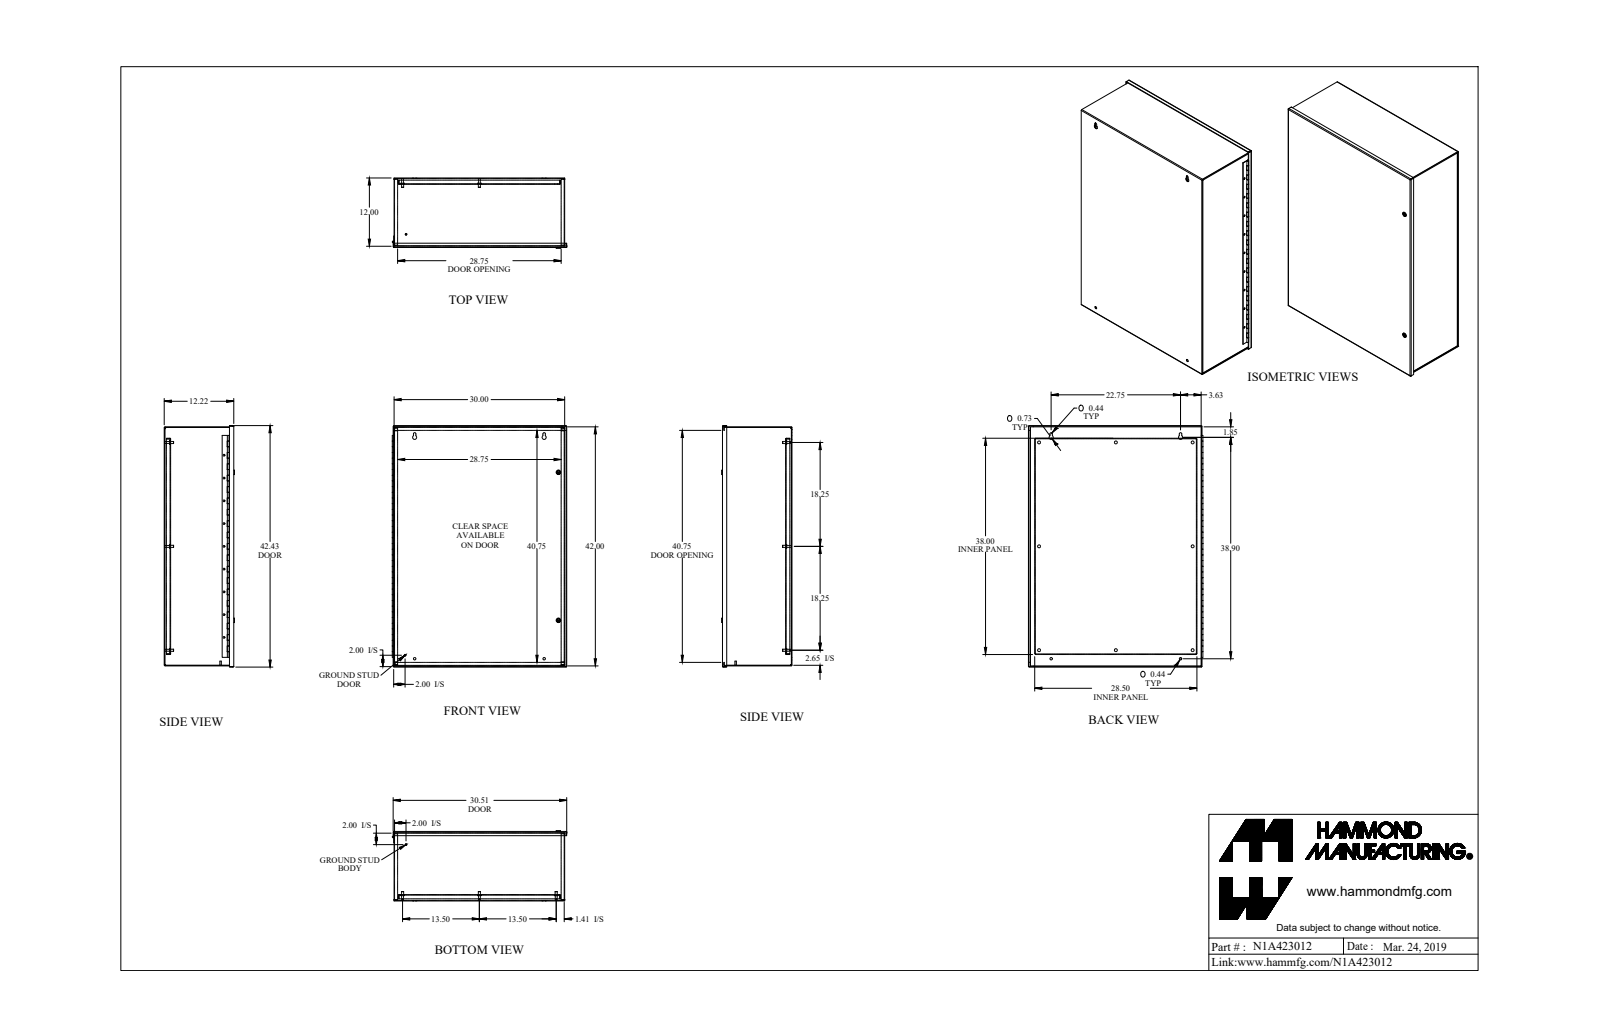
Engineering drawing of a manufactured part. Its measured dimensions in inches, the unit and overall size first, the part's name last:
Units: inches
Overall size (bounding box): 42.43 × 30.668 × 12.342
Round holes (diameter × count): ⌀0.304 ×9, ⌀0.5 ×8, ⌀0.307 ×4, ⌀0.445 ×4, ⌀0.734 ×3, ⌀0.437 ×2, ⌀0.516 ×2, ⌀0.188 ×1
Round bosses / shafts (diameter × count): ⌀0.65 ×8, ⌀0.375 ×8, ⌀0.33 ×8, ⌀1 ×4, ⌀0.788 ×2, ⌀0.535 ×2, ⌀0.496 ×2, ⌀0.281 ×2
Partial cylindrical surfaces — rounded edges, fillets, slot ends (radius × count): R0.048 ×16, R0.143 ×16, R0.125 ×6, R0.03 ×5, R0.219 ×3, R0.06 ×2, R0.153 ×2, R0.315 ×2
Main face-to-face distances: 0.095, 1.032, 0.095, 12.03, 12.125, 12.125, 12.22, 11.093, 1.127, 10.998
Hole centre spacings: 4, 8, 12, 16, 20, 22.699, 24, 26.998
Volume: 545.3 in³ · Surface area: 11 617 in²
Bodies: 31 solids, 951 faces (503 planar, 380 cylindrical, 68 other)
Part name (STEP PRODUCT): N1A423012
STEP written by: SolidWorks 2018 (AUTOMOTIVE_DESIGN)
